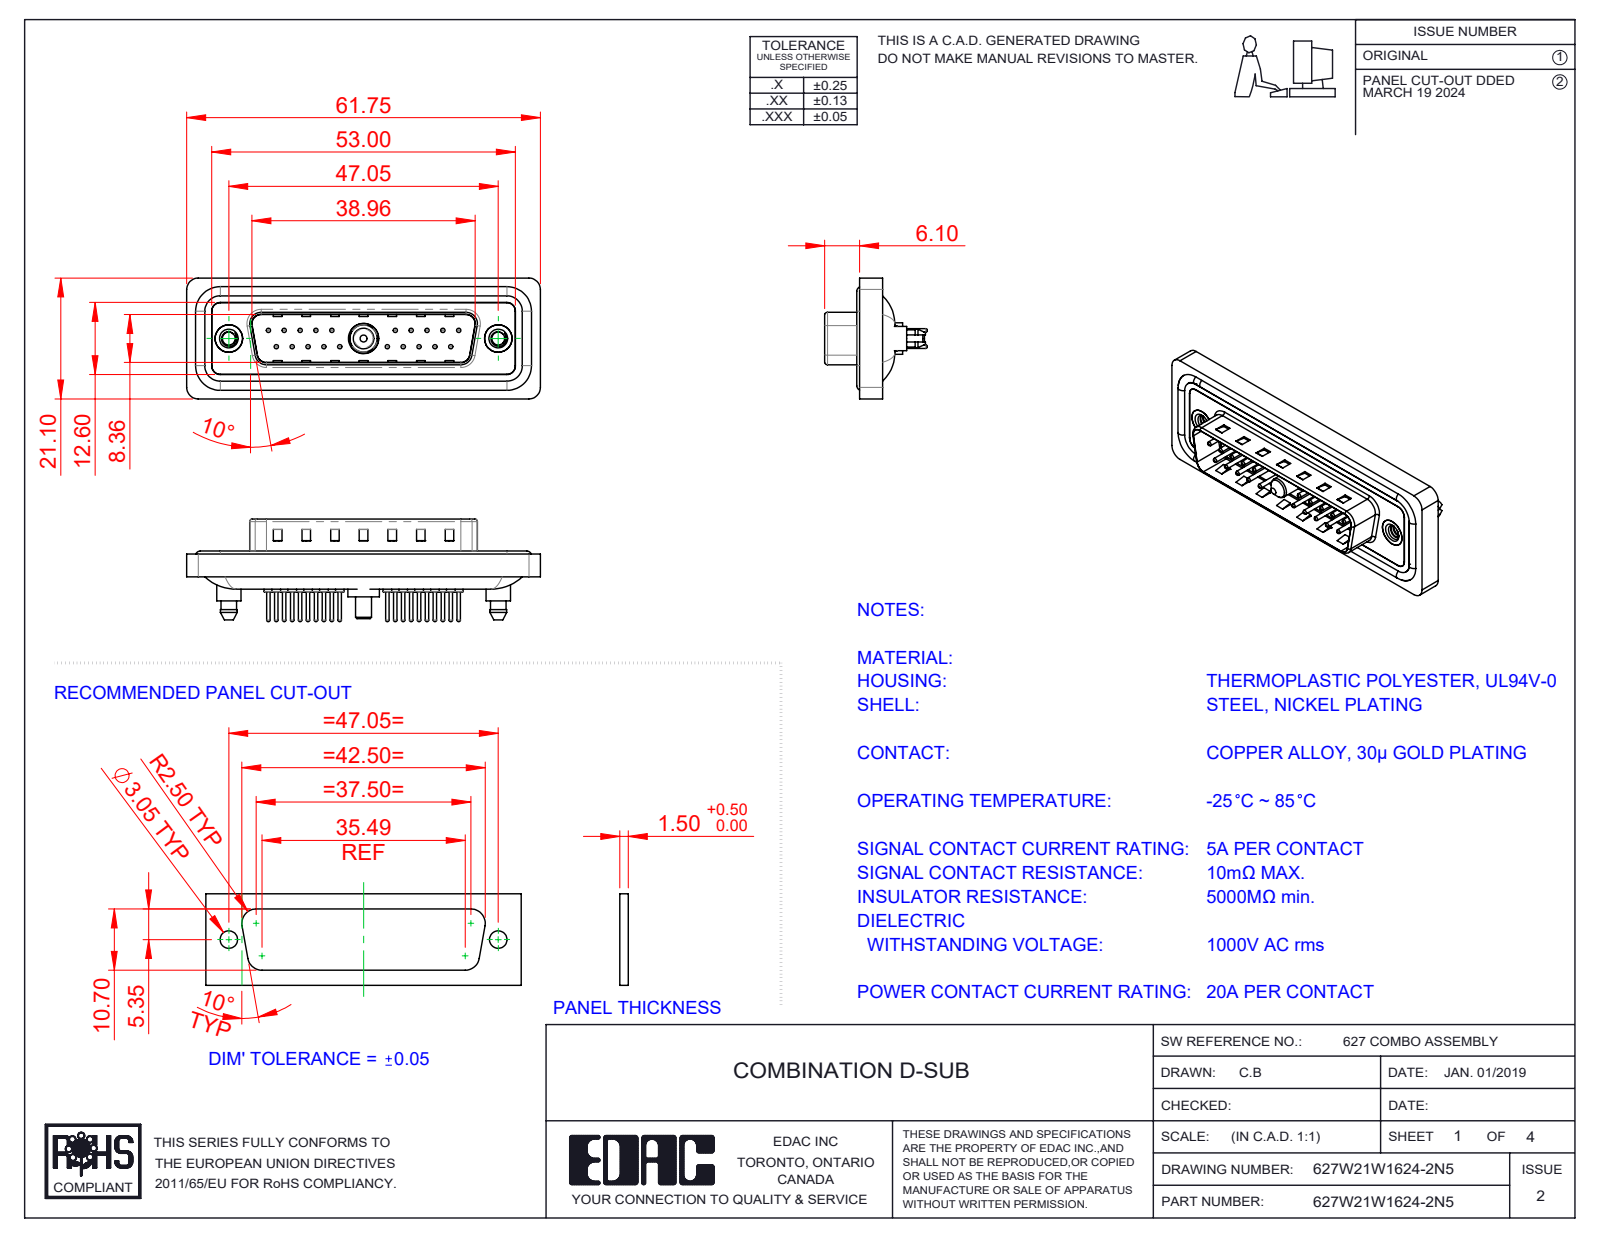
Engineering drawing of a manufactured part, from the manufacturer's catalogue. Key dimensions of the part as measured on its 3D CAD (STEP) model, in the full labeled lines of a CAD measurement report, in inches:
Part name (STEP PRODUCT): 627Combo Waterproof Housing_25 Contacts; 627Combo Contact Row 2_24; 627Combo Housing_21W1; 627Combo Threaded Boardlock_5 (+5 more)
STEP written by: SolidWorks 2023 (CONFIG_CONTROL_DESIGN)
Units: inches
Bodies: 29 solids, 1312 faces (375 planar, 519 cylindrical, 418 other)
Overall size (bounding box): 2.431 × 0.831 × 0.705
Volume: 0.447 in³ · Surface area: 19.04 in²
Round holes (diameter × count): ⌀0.03 ×20, ⌀0.063 ×20, ⌀0.079 ×20, ⌀0.089 ×2, ⌀0.157 ×2, ⌀0.189 ×2, ⌀0.197 ×2, ⌀0.191 ×1, ⌀0.209 ×1
Round bosses / shafts (diameter × count): ⌀0.059 ×20, ⌀0.024 ×20, ⌀0.063 ×4, ⌀0.213 ×2, ⌀0.193 ×2, ⌀0.167 ×2, ⌀0.217 ×1, ⌀0.205 ×1
Partial cylindrical surfaces — rounded edges, fillets, slot ends (radius × count): R0.059 ×24, R0.079 ×18, R0.063 ×10, R0.02 ×8, R0.01 ×4, R0.024 ×4, R0.026 ×4, R0.035 ×4
Main face-to-face distances: 0.016, 0.059, 0.043, 0.063, 0.02, 0.122, 0.114, 0.161, 0.032, 0.377
Hole centre spacings: 0.124, 0.109, 0.218, 0.327, 0.198, 0.763, 0.826, 0.872
